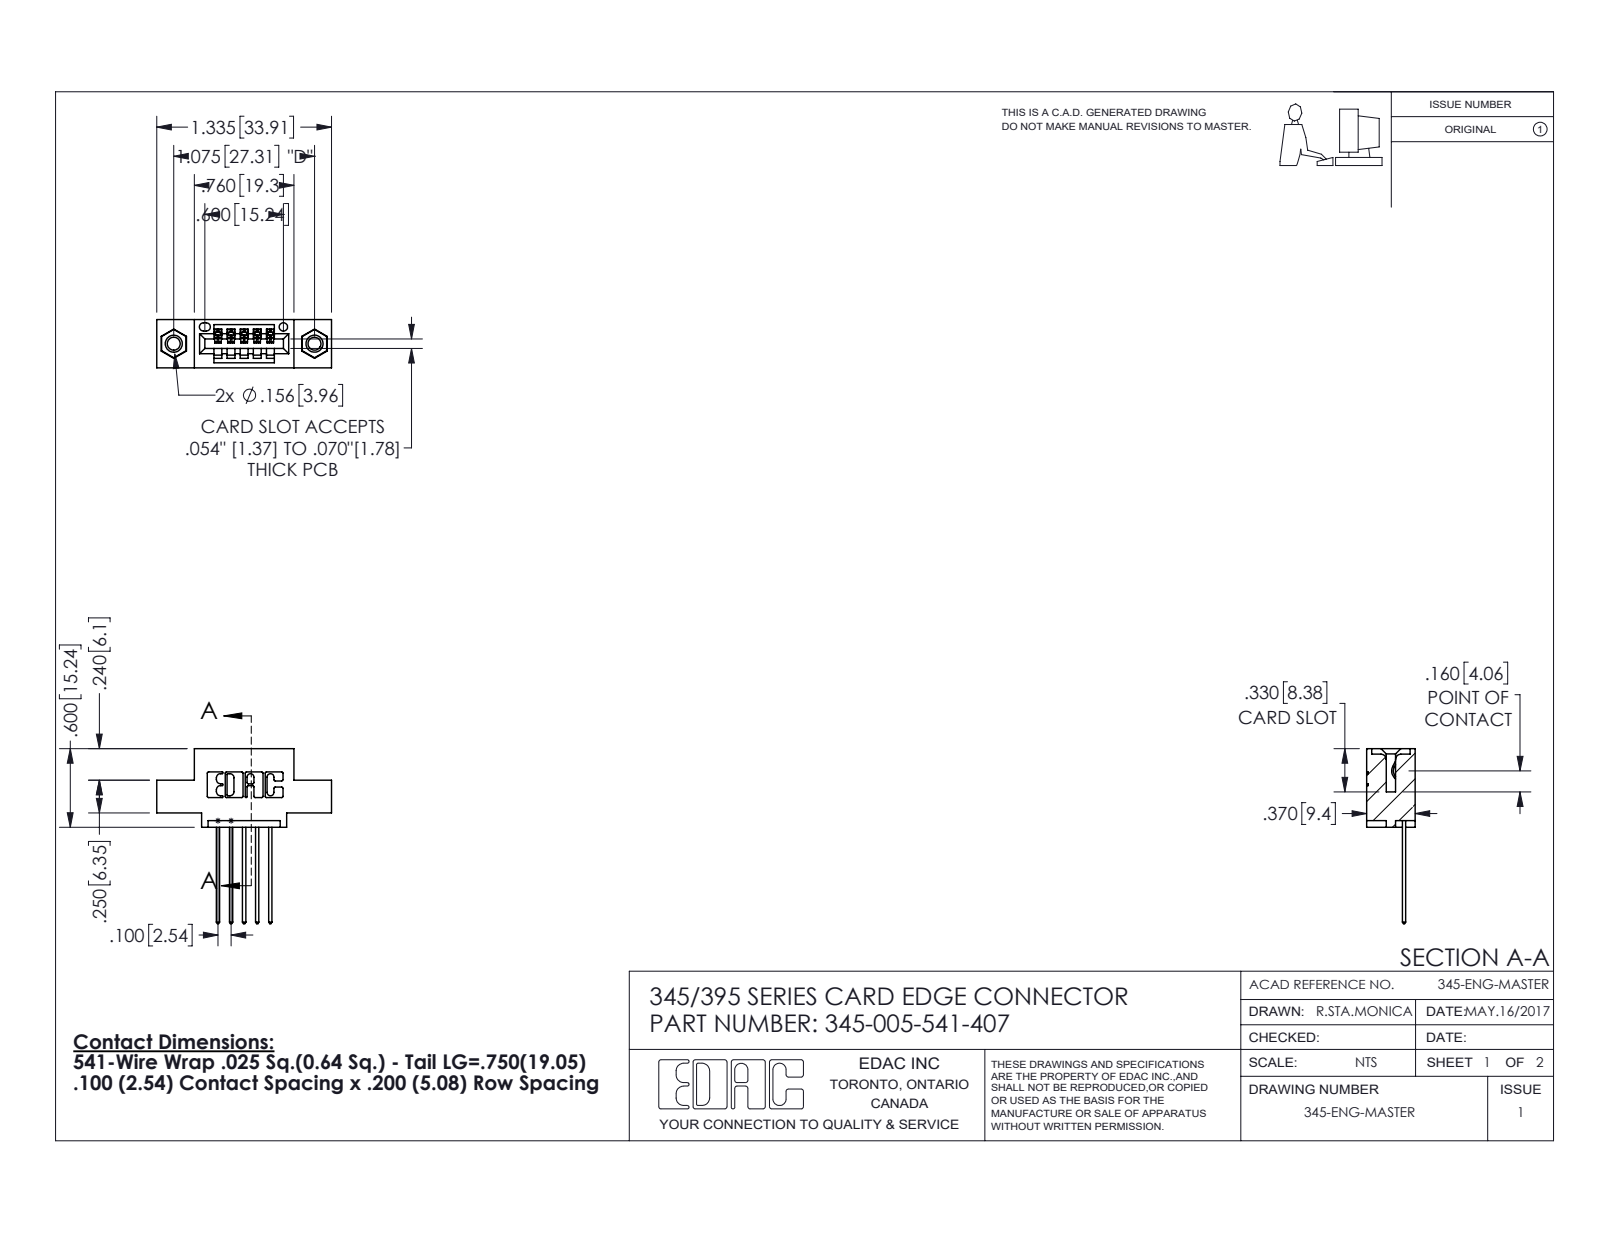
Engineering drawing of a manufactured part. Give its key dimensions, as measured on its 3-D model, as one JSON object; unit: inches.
{"part_name": "345-292-001_345-293-141; 345 Part_0.110 Offset - 0.156 Dia-TI; 345-250-001_345-250-005-103; 345-005-541-407", "step_written_by": "SolidWorks 2016 (CONFIG_CONTROL_DESIGN)", "units": "inches", "bodies": {"solids": 8, "faces": 480, "planar": 316, "cylindrical": 148, "other": 16}, "overall_size": [1.337, 1.335, 0.37], "volume_in3": 0.174, "surface_area_in2": 5.413, "round_holes": [[0.098, 2], [0.125, 2], [0.156, 2], [0.064, 1]], "round_bosses_or_shafts": [[0.155, 2]], "partial_cylinders_radius": [[0.01, 22], [0.006, 10], [0.01, 10], [0.007, 6], [0.031, 6], [0.026, 3], [0.031, 2], [0.04, 2]], "face_to_face_distances": [0.2, 0.37, 0.072, 0.298, 0.1, 0.025, 0.098, 0.272, 0.25, 0.06], "hole_center_spacings": [0.27, 0.847, 1.075]}
